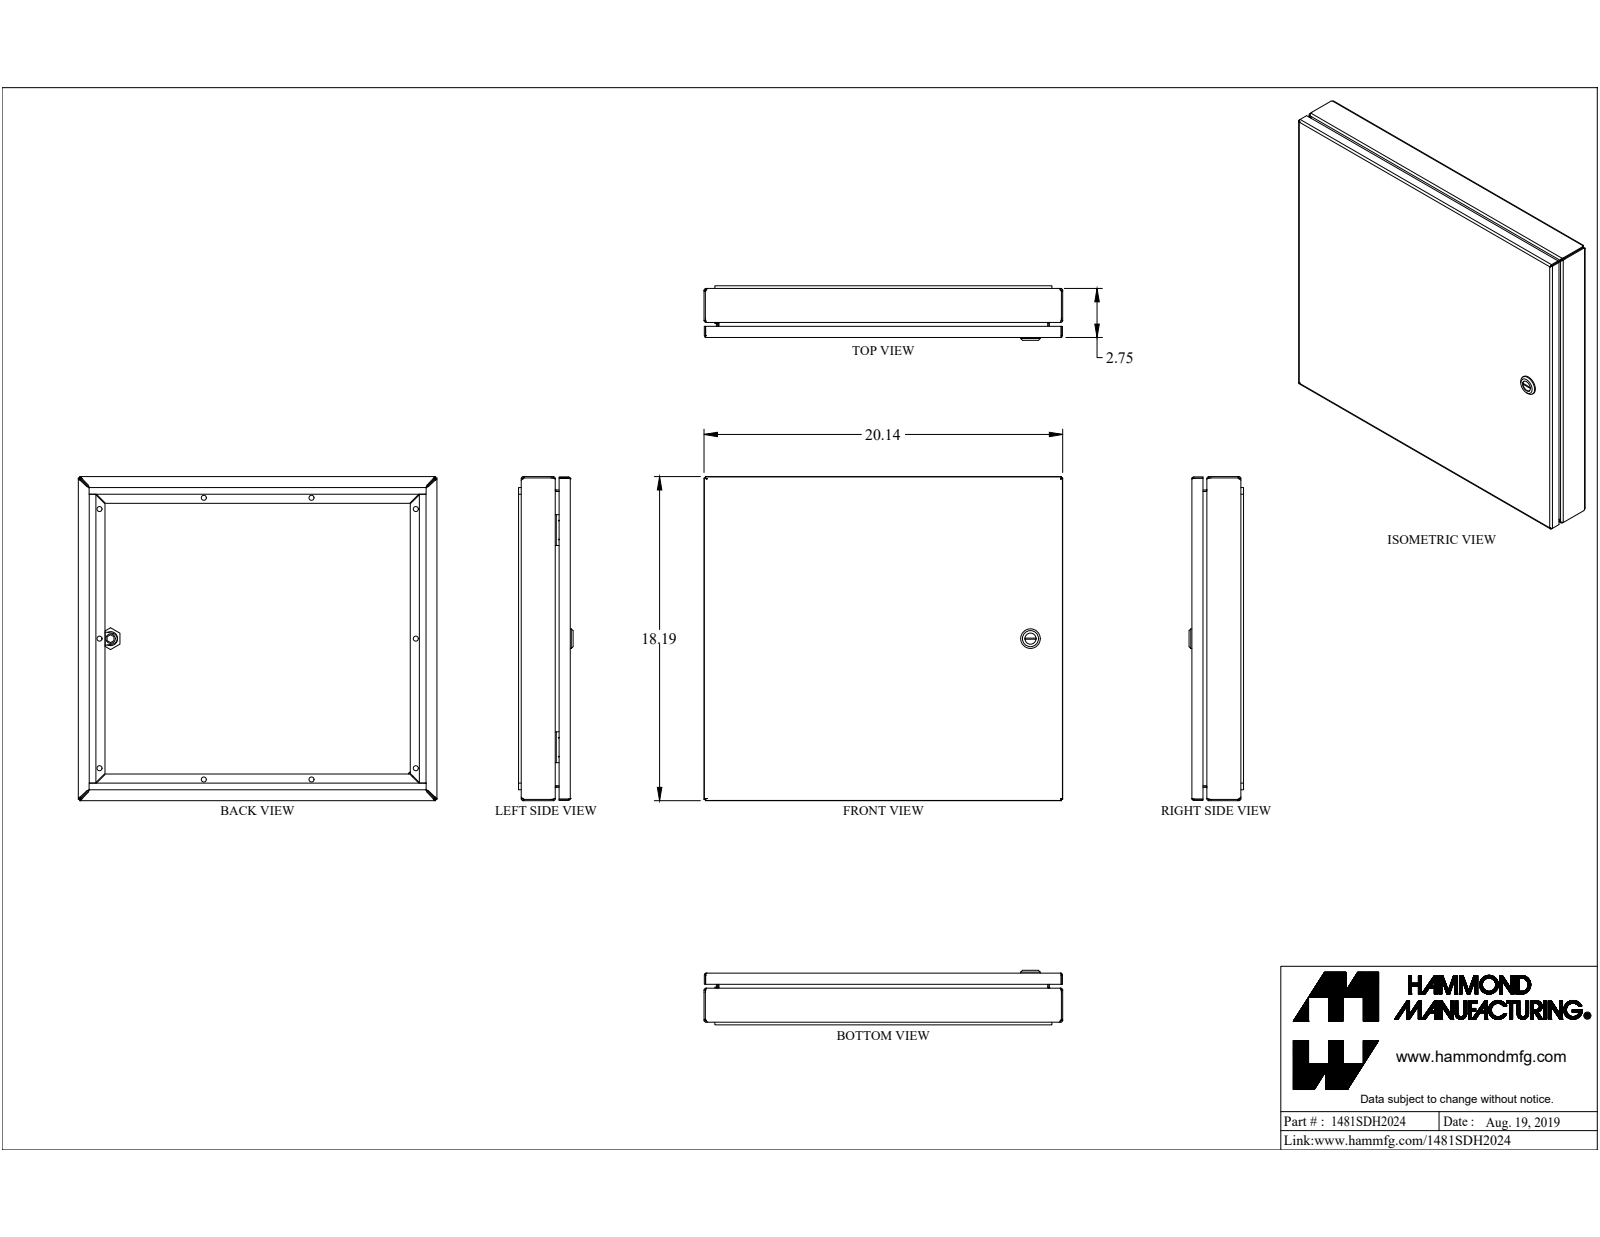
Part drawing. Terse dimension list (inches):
name: 1481SDH2024
written by: SolidWorks 2019 (CONFIG_CONTROL_DESIGN)
unit: in
bodies: 23 solids, 616 faces (348 planar, 170 cylindrical, 98 other)
size: 20.14 × 18.19 × 3.061
volume: 68.54 in³; area: 1 791 in²
holes: 10× ⌀0.281, 1× ⌀0.172, 1× ⌀0.232, 1× ⌀0.24, 1× ⌀0.242, 1× ⌀0.625, 1× ⌀0.785
bosses: 1× ⌀1.1, 1× ⌀0.525, 1× ⌀0.455, 1× ⌀0.455, 1× ⌀0.398, 1× ⌀0.356, 1× ⌀0.313, 1× ⌀0.292
rounds: 28× R0.036, 28× R0.108, 12× R0.382, 8× R19.003, 4× R0.006, 4× R0.062, 4× R0.25, 4× R0.499
face distances: 0.072, 2.579, 0.843, 1.736, 2.651, 18.118, 20.068, 2.507, 2.679, 1.836
hole spacings: 5.893, 11.922, 14.291, 16.271, 19.291, 17.764, 6.046, 7.273
